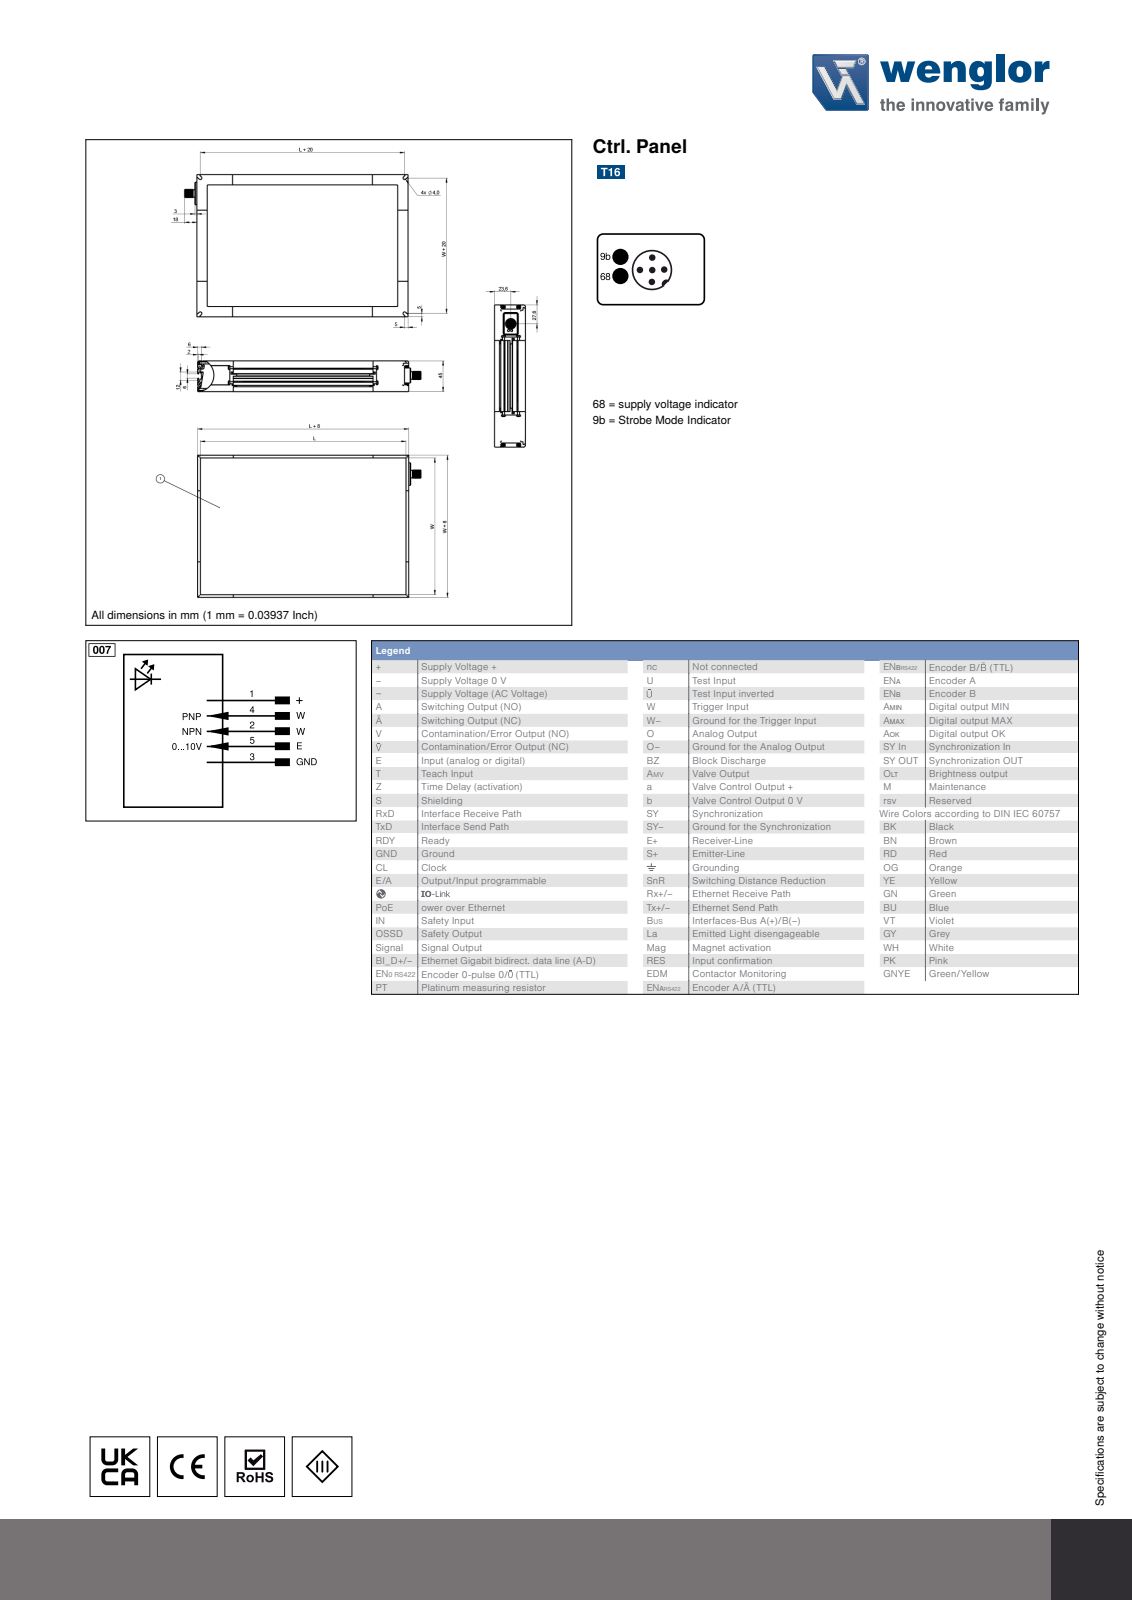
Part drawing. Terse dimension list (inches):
name: OPT2422 and OPT2423_REV
written by: SolidWorks 2021 (AUTOMOTIVE_DESIGN)
unit: in
bodies: 1 solid, 242 faces (133 planar, 97 cylindrical, 12 other)
size: 16.768 × 16.063 × 1.791
volume: 419.7 in³; area: 683.3 in²
holes: 2× ⌀0.118, 1× ⌀0.327
bosses: 8× ⌀0.22, 5× ⌀0.039, 1× ⌀0.472, 1× ⌀0.423
rounds: 20× R0.02, 4× R0.089, 4× R0.118, 4× R0.197, 1× R0.024
face distances: 1.648, 16.063, 0.079, 1.726, 15.843, 0.157, 0.24, 15.823, 0.22, 0.02
hole spacings: 0.183, 0.394, 0.41
